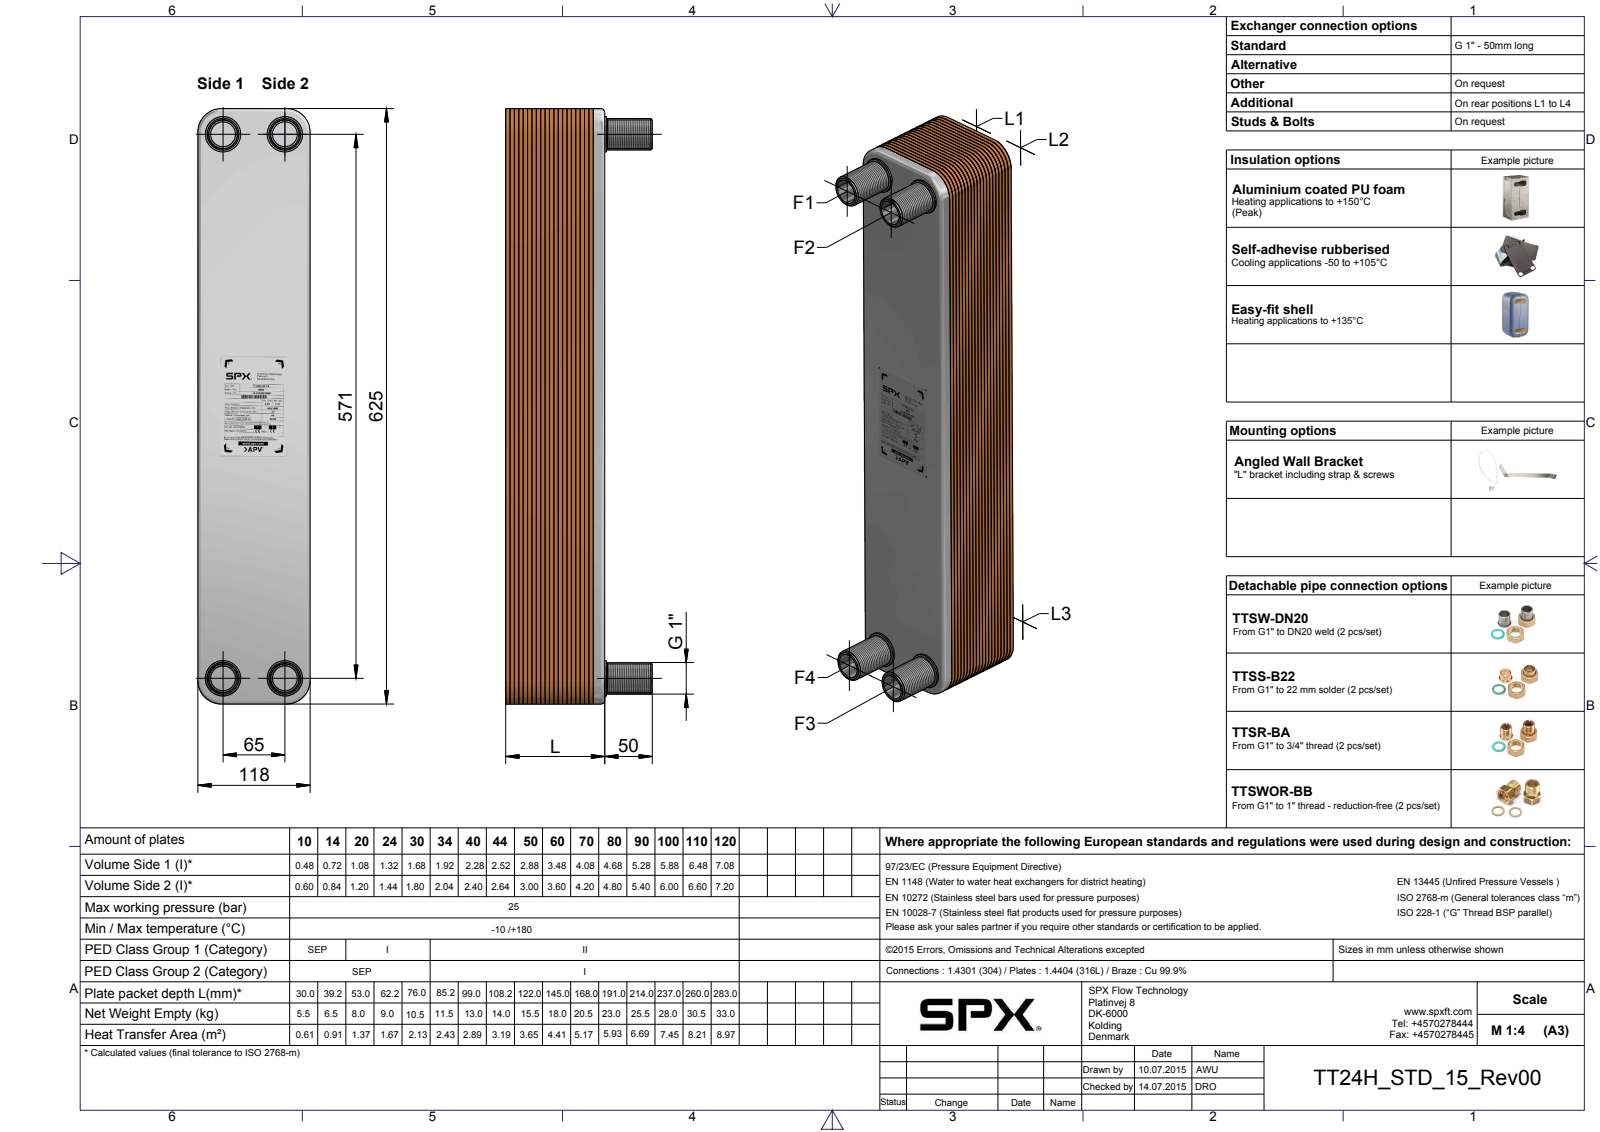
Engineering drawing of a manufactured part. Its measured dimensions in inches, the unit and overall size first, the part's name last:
Units: inches
Overall size (bounding box): 24.606 × 7.677 × 4.646
Round holes (diameter × count): ⌀1.024 ×4
Round bosses / shafts (diameter × count): ⌀1.465 ×4, ⌀1.307 ×4
Partial cylindrical surfaces — rounded edges, fillets, slot ends (radius × count): R0.157 ×4, R0.984 ×4
Main face-to-face distances: 0.181, 0.362, 0.543, 0.724, 0.906, 1.087, 1.268, 1.449, 1.63, 1.811
Hole centre spacings: 2.559, 22.48, 22.626
Volume: 468.5 in³ · Surface area: 5 081 in²
Bodies: 26 solids, 424 faces (232 planar, 100 cylindrical, 92 other)
Part name (STEP PRODUCT): Grundplatte; Anschluss G2; Kupferplatte; PB24_Typenschild (+1 more)
STEP written by: Autodesk Inventor 2016 (AUTOMOTIVE_DESIGN)
